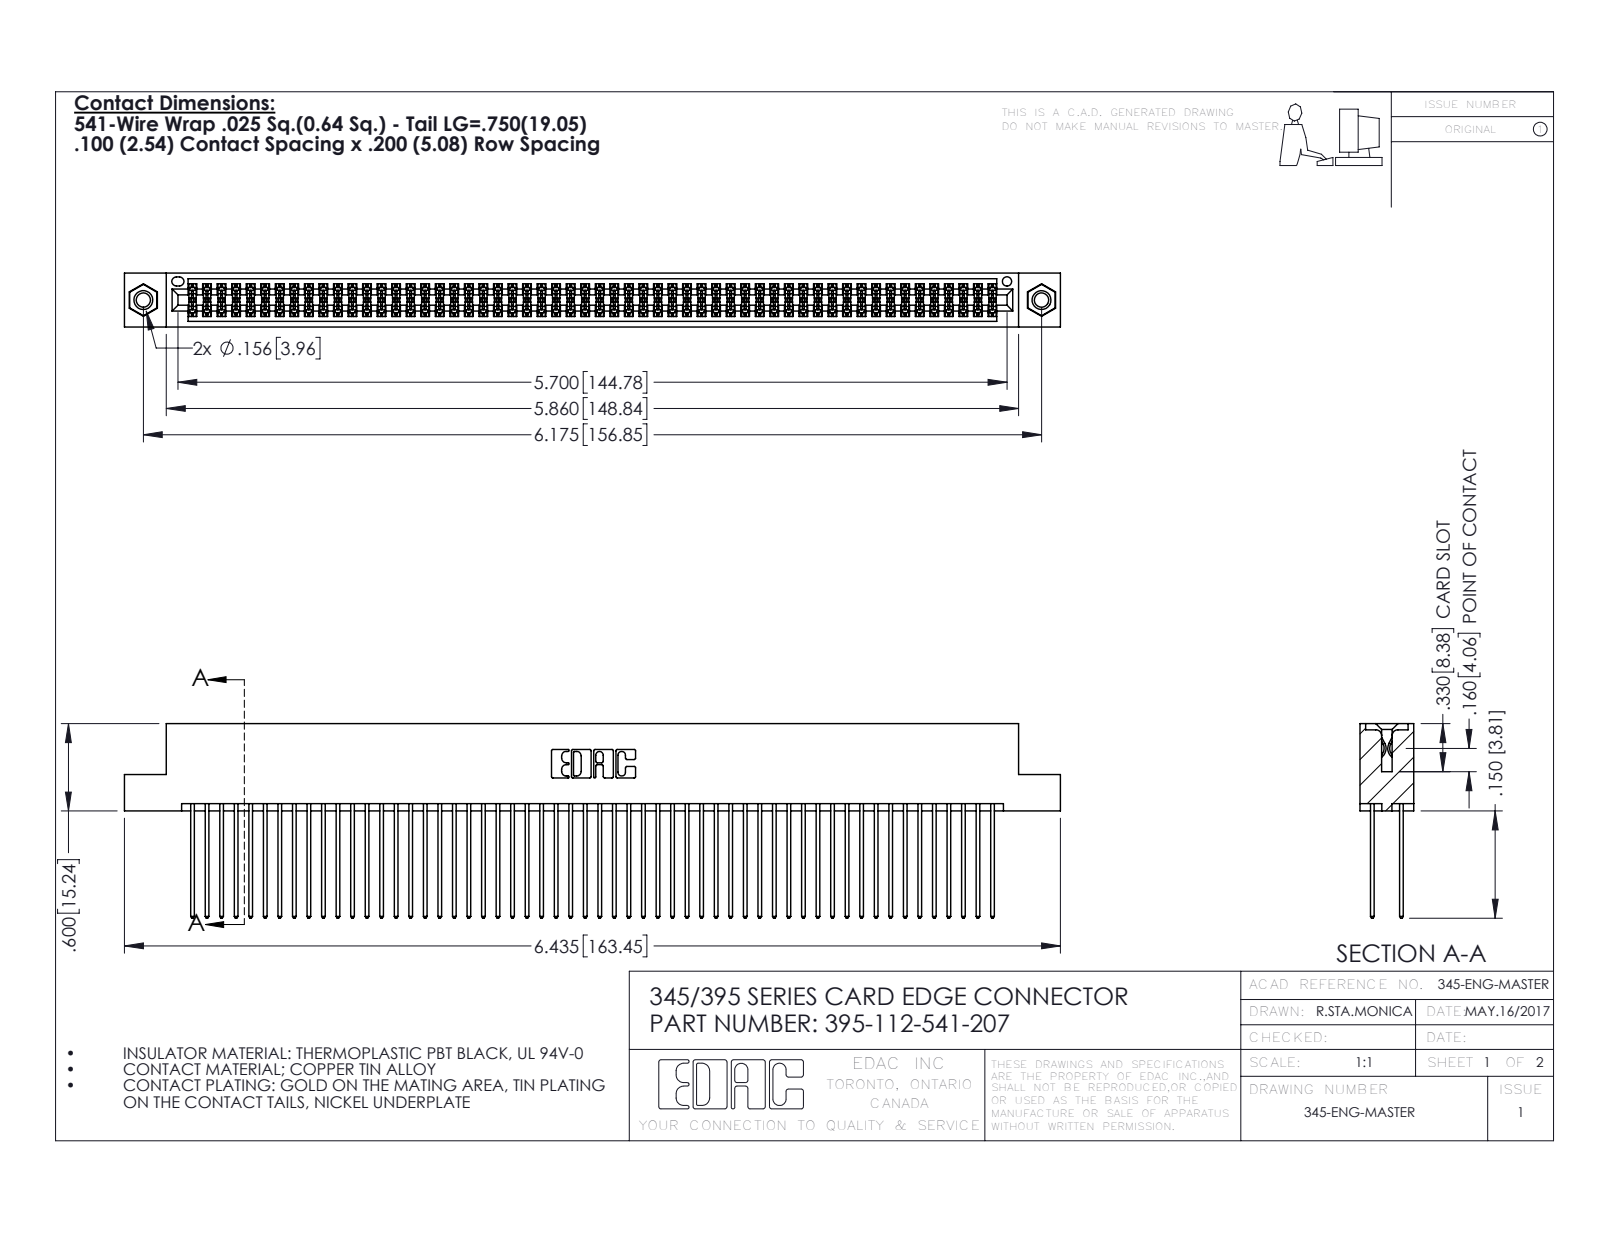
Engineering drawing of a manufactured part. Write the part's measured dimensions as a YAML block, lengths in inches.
part_name: "345-292-001_345-293-141; 345-250-001_345-250-005-103; 395-112-541-207; 345 Part_Flush Mounting Lugs - 0.156 Dia-TI"
step_written_by: "SolidWorks 2016 (CONFIG_CONTROL_DESIGN)"
units: inches
bodies: {solids: 115, faces: 5786, planar: 3808, cylindrical: 1962, other: 16}
overall_size: [6.435, 1.337, 0.37]
volume: 1.015
surface_area: 43.26
round_holes:
  - {diameter: 0.098, count: 2}
  - {diameter: 0.125, count: 2}
  - {diameter: 0.156, count: 2}
  - {diameter: 0.064, count: 1}
round_bosses_or_shafts:
  - {diameter: 0.155, count: 2}
partial_cylinders:
  - {radius: 0.006, count: 168}
  - {radius: 0.01, count: 112}
  - {radius: 0.01, count: 22}
  - {radius: 0.007, count: 6}
  - {radius: 0.031, count: 6}
  - {radius: 0.026, count: 3}
  - {radius: 0.014, count: 2}
  - {radius: 0.019, count: 2}
face_to_face_distances: [0.072, 0.298, 0.2, 0.098, 0.272, 0.025, 0.225, 0.37, 0.175, 0.149]
hole_center_spacings: [0.27, 5.939, 6.175]
